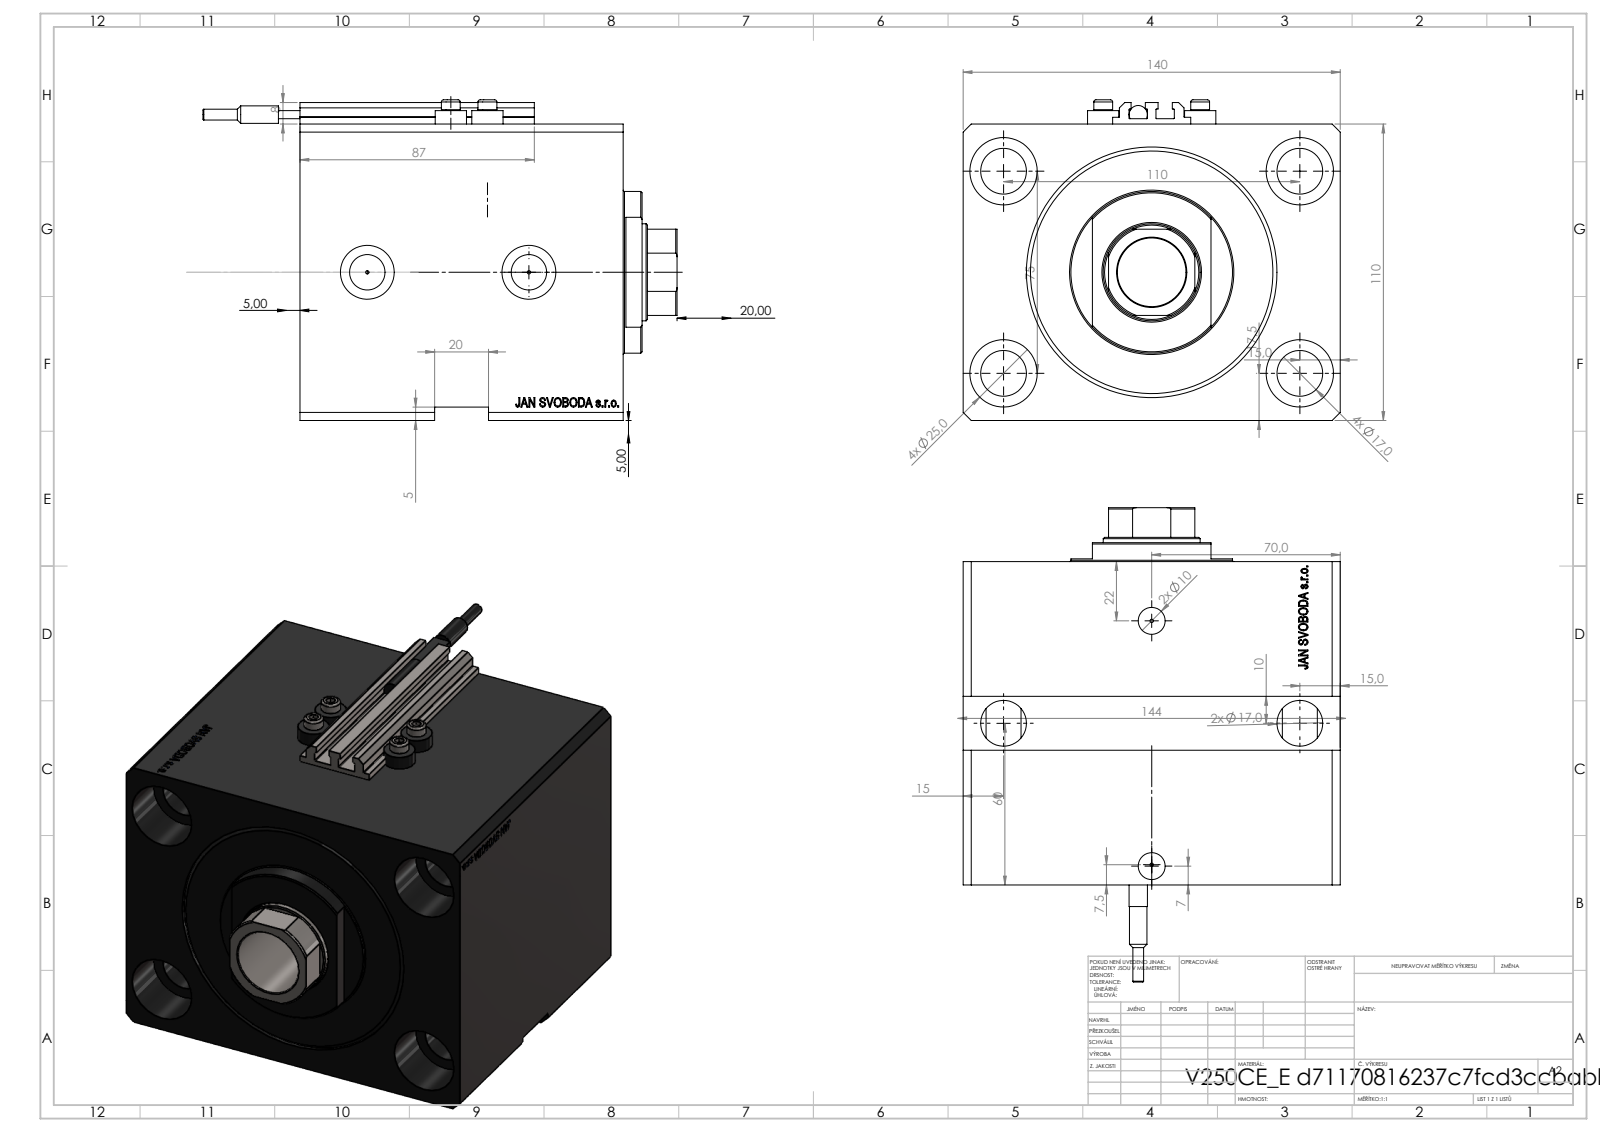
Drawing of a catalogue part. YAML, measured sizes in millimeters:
part_name: "V250CE_E; V250CE_VC_E; SWITCH_V250CE; V250CE_C_VCP (+1 more)"
step_written_by: "SolidWorks 2019 (CONFIG_CONTROL_DESIGN)"
units: millimeters
bodies: {solids: 9, faces: 1138, planar: 564, cylindrical: 132, other: 442}
overall_size: [176, 140, 119]
volume: 1593000
surface_area: 222619
round_holes:
  - {diameter: 17, count: 6}
  - {diameter: 1.25, count: 4}
  - {diameter: 4, count: 4}
  - {diameter: 25, count: 4}
  - {diameter: 10, count: 2}
  - {diameter: 13.16, count: 2}
  - {diameter: 20, count: 2}
  - {diameter: 25.5, count: 1}
  - {diameter: 36, count: 1}
  - {diameter: 80, count: 1}
  - {diameter: 93, count: 1}
round_bosses_or_shafts:
  - {diameter: 11.6, count: 4}
  - {diameter: 7, count: 4}
  - {diameter: 60, count: 1}
  - {diameter: 6.8, count: 1}
  - {diameter: 6.5, count: 1}
  - {diameter: 4, count: 1}
partial_cylinders:
  - {radius: 0.2, count: 10}
  - {radius: 17.5, count: 1}
face_to_face_distances: [110, 140, 25, 95, 120, 33, 62, 87, 53, 20]
hole_center_spacings: [66.57, 110, 13.6, 33.62, 36, 37.22, 38.23, 38.48]
